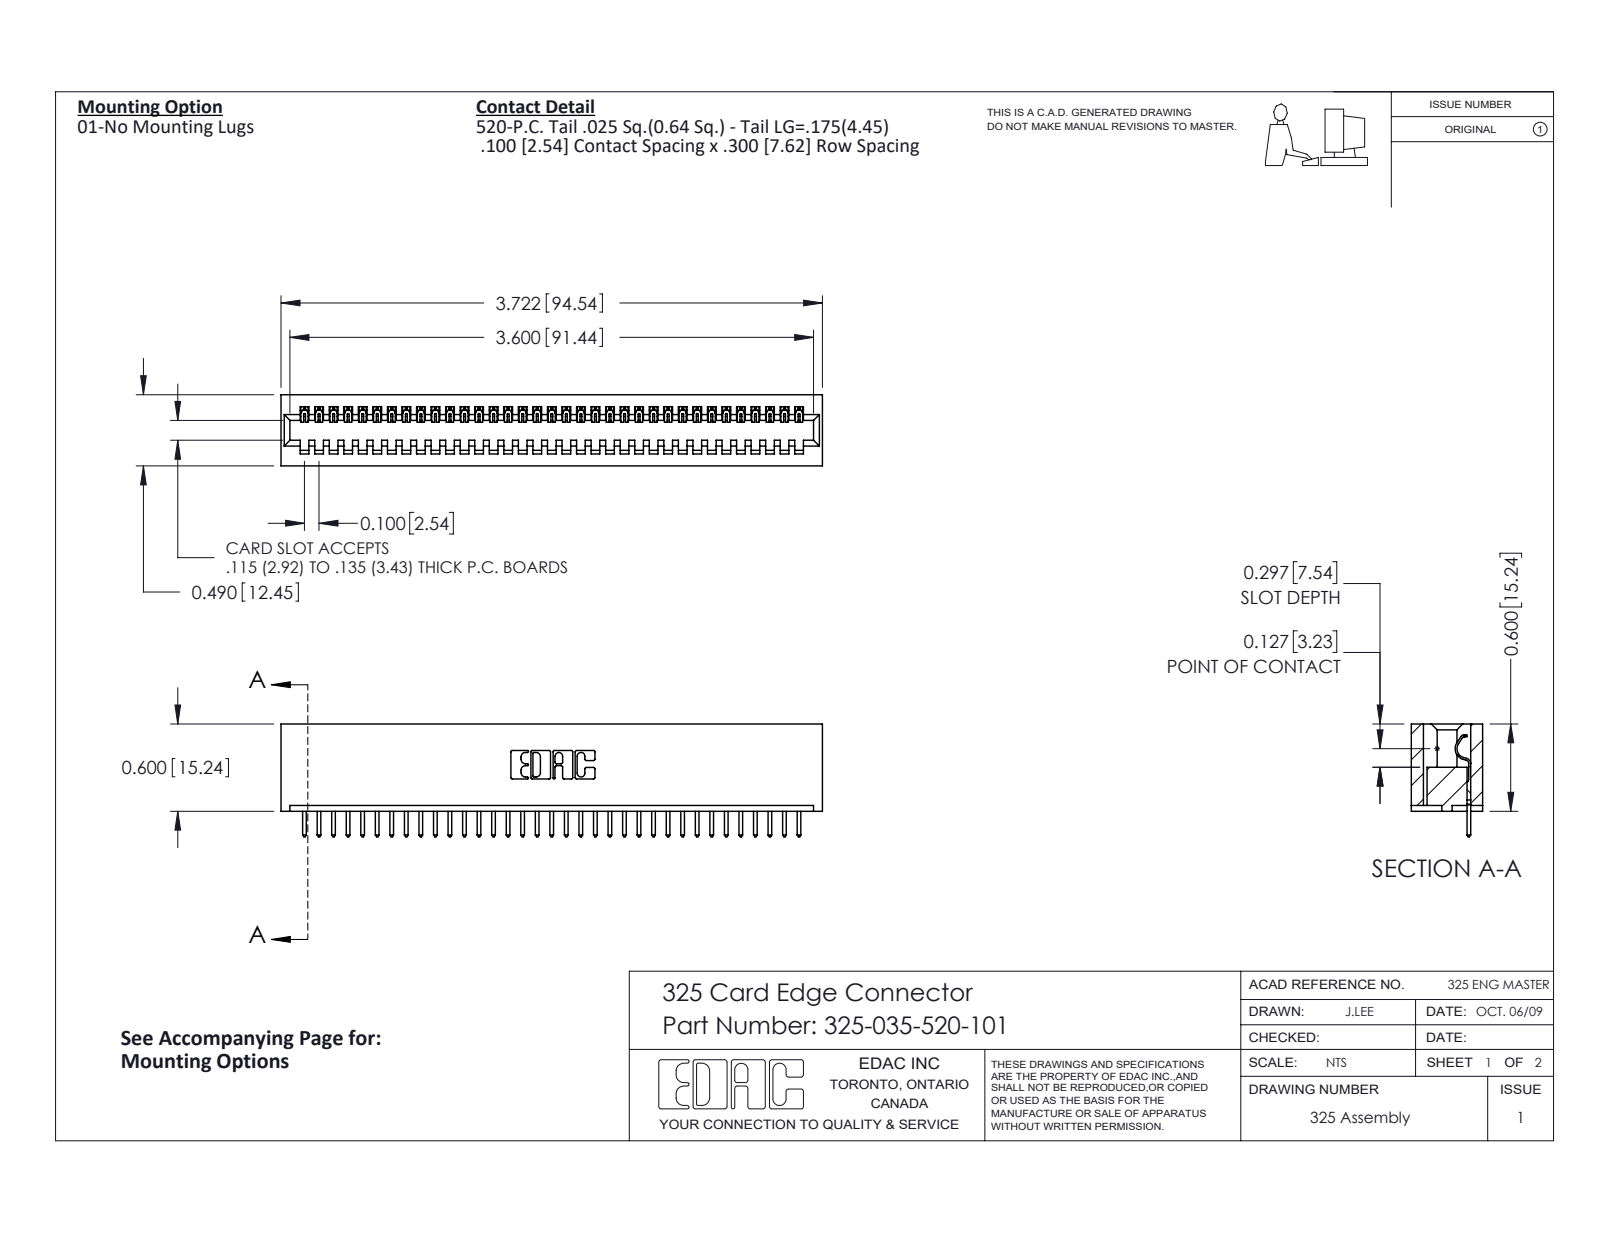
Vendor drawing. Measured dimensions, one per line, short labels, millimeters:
name: 325-035-520-101; 325-292-001_325-293-120; 325 Part_Lugless
written by: SolidWorks 2016 (CONFIG_CONTROL_DESIGN)
unit: mm
bodies: 36 solids, 2136 faces (1536 planar, 600 cylindrical, 0 other)
size: 94.5 × 19.7 × 12.4
volume: 12 400 mm³; area: 13 580 mm²
rounds: 70× R0.2, 70× R0.3, 22× R0.3, 6× R0.2, 6× R0.8, 3× R0.7, 1× R0.4, 1× R0.6
face distances: 2.1, 10.3, 12.4, 7.6, 2.7, 9.7, 0.6, 8.3, 14.2, 6.7
